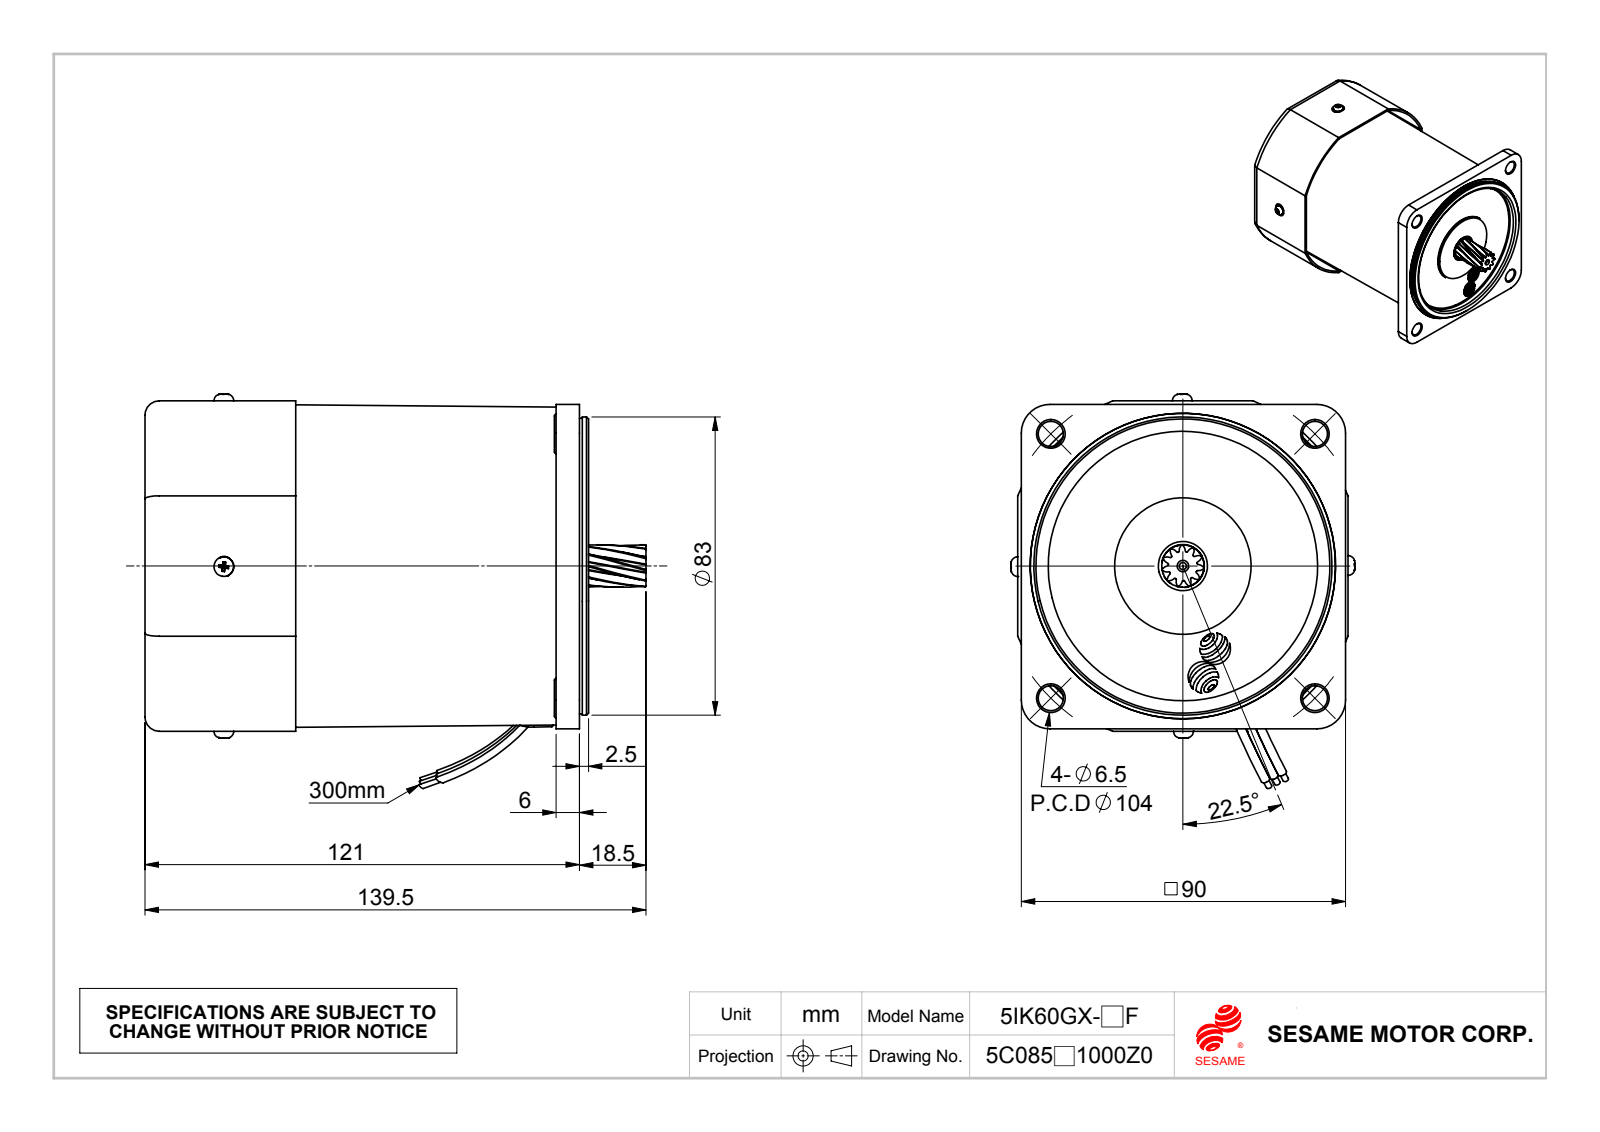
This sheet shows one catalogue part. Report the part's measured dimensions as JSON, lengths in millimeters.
{"part_name": "60GX; 線扣; M560; 風扇蓋FC-9042-21", "step_written_by": "SolidWorks 2010 (CONFIG_CONTROL_DESIGN)", "units": "millimeters", "bodies": {"solids": 12, "faces": 721, "planar": 209, "cylindrical": 335, "other": 177}, "overall_size": [139.5, 109.84, 95.83], "volume_mm3": 682963, "surface_area_mm2": 101761, "round_holes": [[2.5, 5], [7, 4], [2, 1], [6.5, 1], [7.2, 1], [9.5, 1], [13.7, 1], [24, 1], [26, 1], [40, 1], [54, 1], [58.1, 1]], "round_bosses_or_shafts": [[5.5, 4], [3, 4], [84.22, 1], [83, 1], [82.2, 1], [47, 1], [38, 1], [31, 1]], "partial_cylinders_radius": [[0.3, 16], [0.25, 8], [0.78, 8], [1, 8], [1.5, 8], [1.66, 8], [2.92, 8], [0.2, 4]], "face_to_face_distances": [1, 118.5, 91, 16, 102.5, 118.4, 119.4, 0.9, 117.5, 119.5], "hole_center_spacings": [52, 73.54, 104]}
